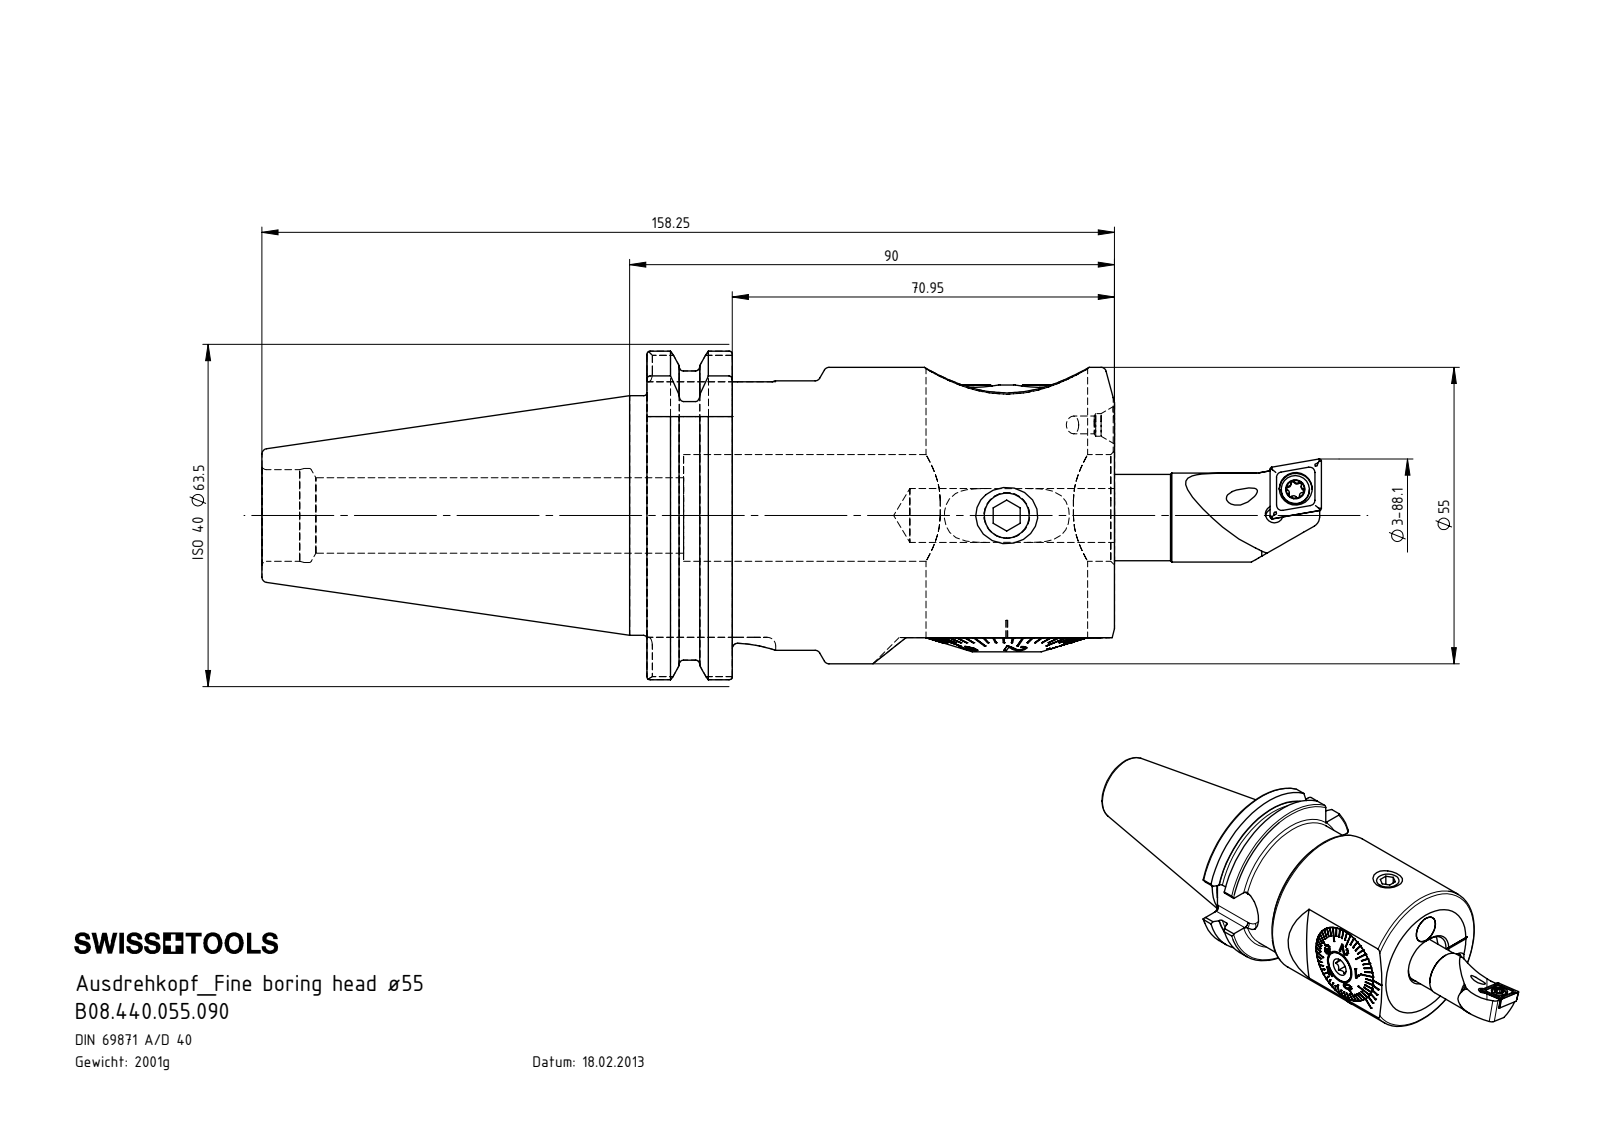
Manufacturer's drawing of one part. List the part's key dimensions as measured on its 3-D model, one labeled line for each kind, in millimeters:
Part name (STEP PRODUCT): A55-BG1.014.041; A55-BG2.015.007_B; B08.440.055.090; A55-BG2.014.007_A (+8 more)
STEP written by: SolidWorks 2017 (CONFIG_CONTROL_DESIGN)
Units: millimetres
Bodies: 19 solids, 956 faces (390 planar, 194 cylindrical, 372 other)
Overall size (bounding box): 196.66 × 63.5 × 60.94
Volume: 255 189 mm³ · Surface area: 63 680 mm²
Round holes (diameter × count): ⌀3.3 ×3, ⌀8.5 ×3, ⌀3 ×2, ⌀14 ×2, ⌀1 ×1, ⌀1.6 ×1, ⌀2 ×1, ⌀4.2 ×1, ⌀4.4 ×1, ⌀6.1 ×1, ⌀8 ×1, ⌀10 ×1
Round bosses / shafts (diameter × count): ⌀10 ×3, ⌀5.25 ×2, ⌀4 ×2, ⌀55 ×1, ⌀50 ×1, ⌀44.45 ×1, ⌀30 ×1, ⌀29.98 ×1
Partial cylindrical surfaces — rounded edges, fillets, slot ends (radius × count): R0.34 ×12, R0.59 ×12, R1.6 ×8, R3.2 ×3, R0.5 ×1, R2 ×1, R3.5 ×1, R8 ×1
Main face-to-face distances: 86.8, 15.85, 70.95, 5.3, 6.48, 1.18, 2.8, 2.5, 3.68, 22
Hole centre spacings: 14.5, 7.25, 0.37, 6.07, 6.19, 14.7, 15.07, 18.83
